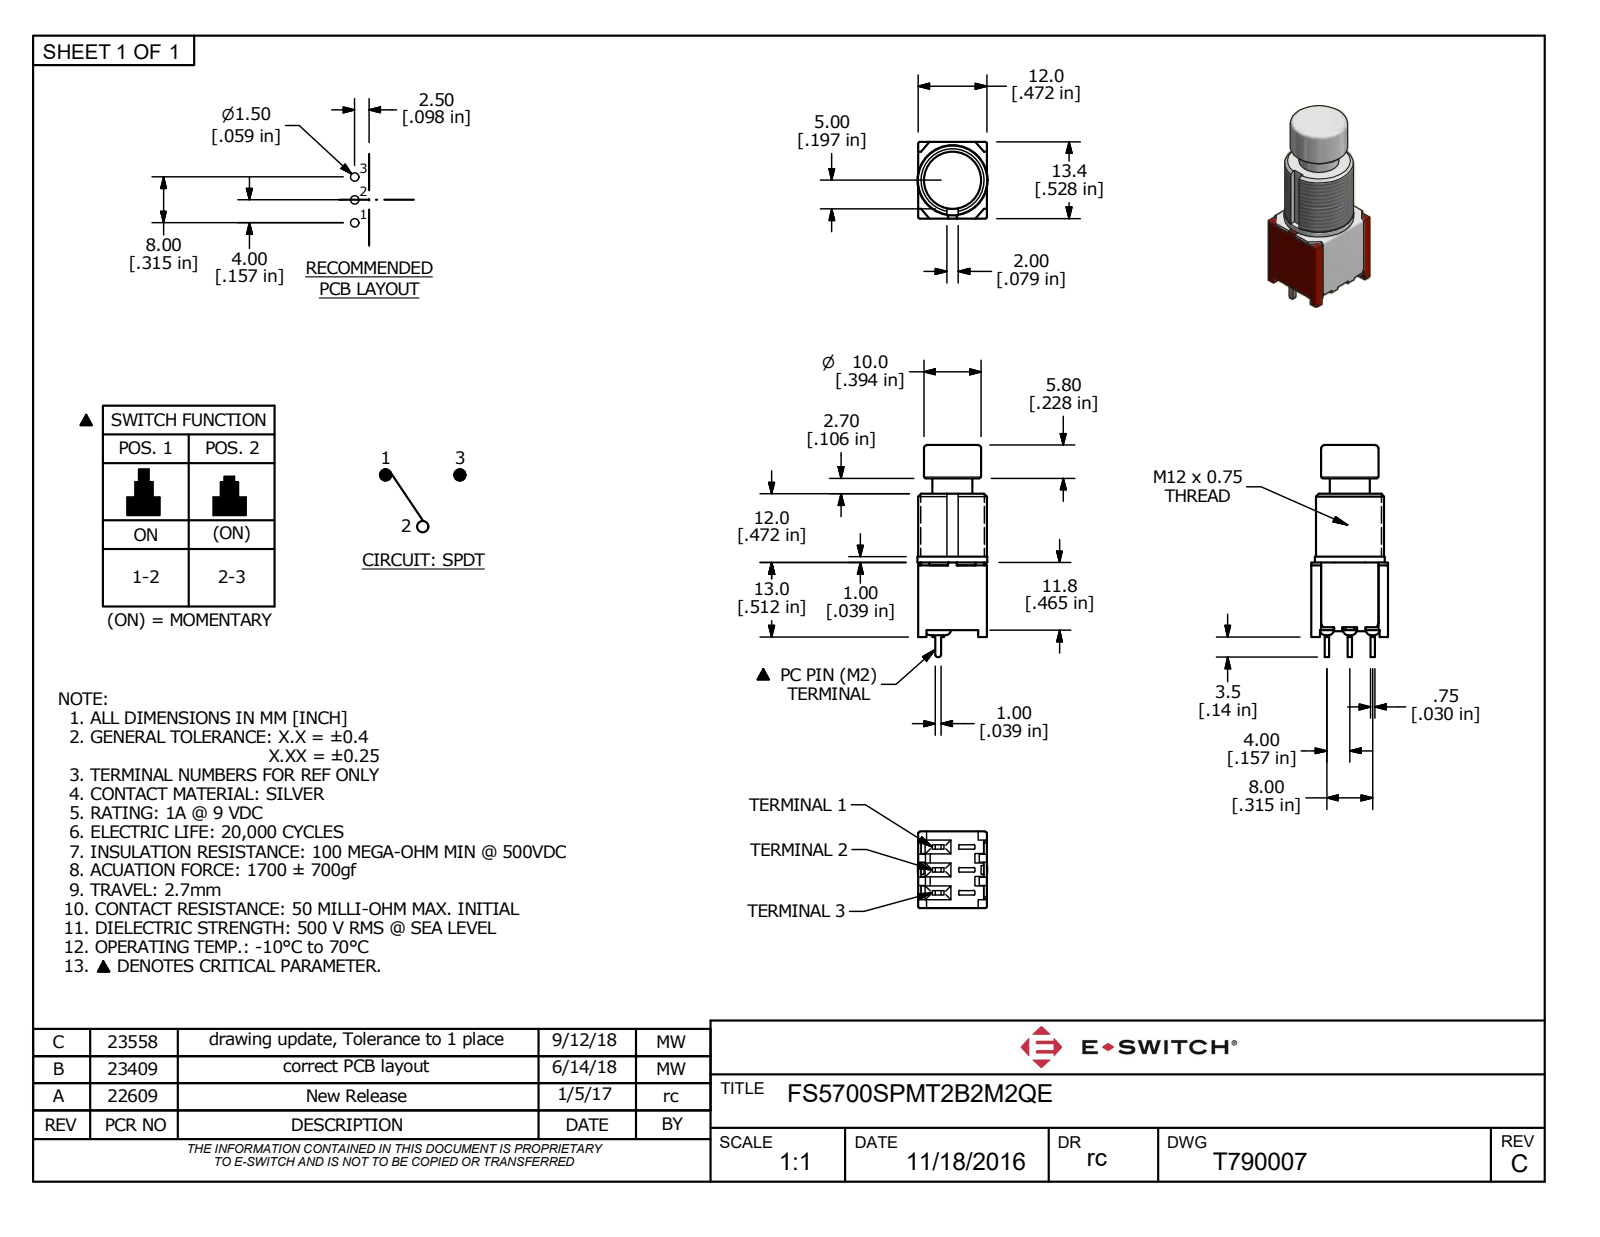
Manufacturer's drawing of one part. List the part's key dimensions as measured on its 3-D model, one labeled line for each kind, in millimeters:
Part name (STEP PRODUCT): FS5700SPMT2B2M2QE
STEP written by: Autodesk Inventor 2018 (AUTOMOTIVE_DESIGN)
Units: millimetres
Bodies: 1 solid, 277 faces (209 planar, 65 cylindrical, 3 other)
Overall size (bounding box): 37 × 13.4 × 12.2
Volume: 2 100 mm³ · Surface area: 3 258 mm²
Round holes (diameter × count): ⌀9 ×1
Round bosses / shafts (diameter × count): ⌀12.2 ×1, ⌀12 ×1, ⌀10 ×1, ⌀7 ×1
Partial cylindrical surfaces — rounded edges, fillets, slot ends (radius × count): R0.2 ×26, R0.9 ×8, R0.3 ×4, R0.5 ×4, R0.1 ×2, R0.4 ×2
Main face-to-face distances: 1.2, 0.5, 11, 10.8, 10.3, 0.7, 11.5, 0.55, 11.45, 0.65
